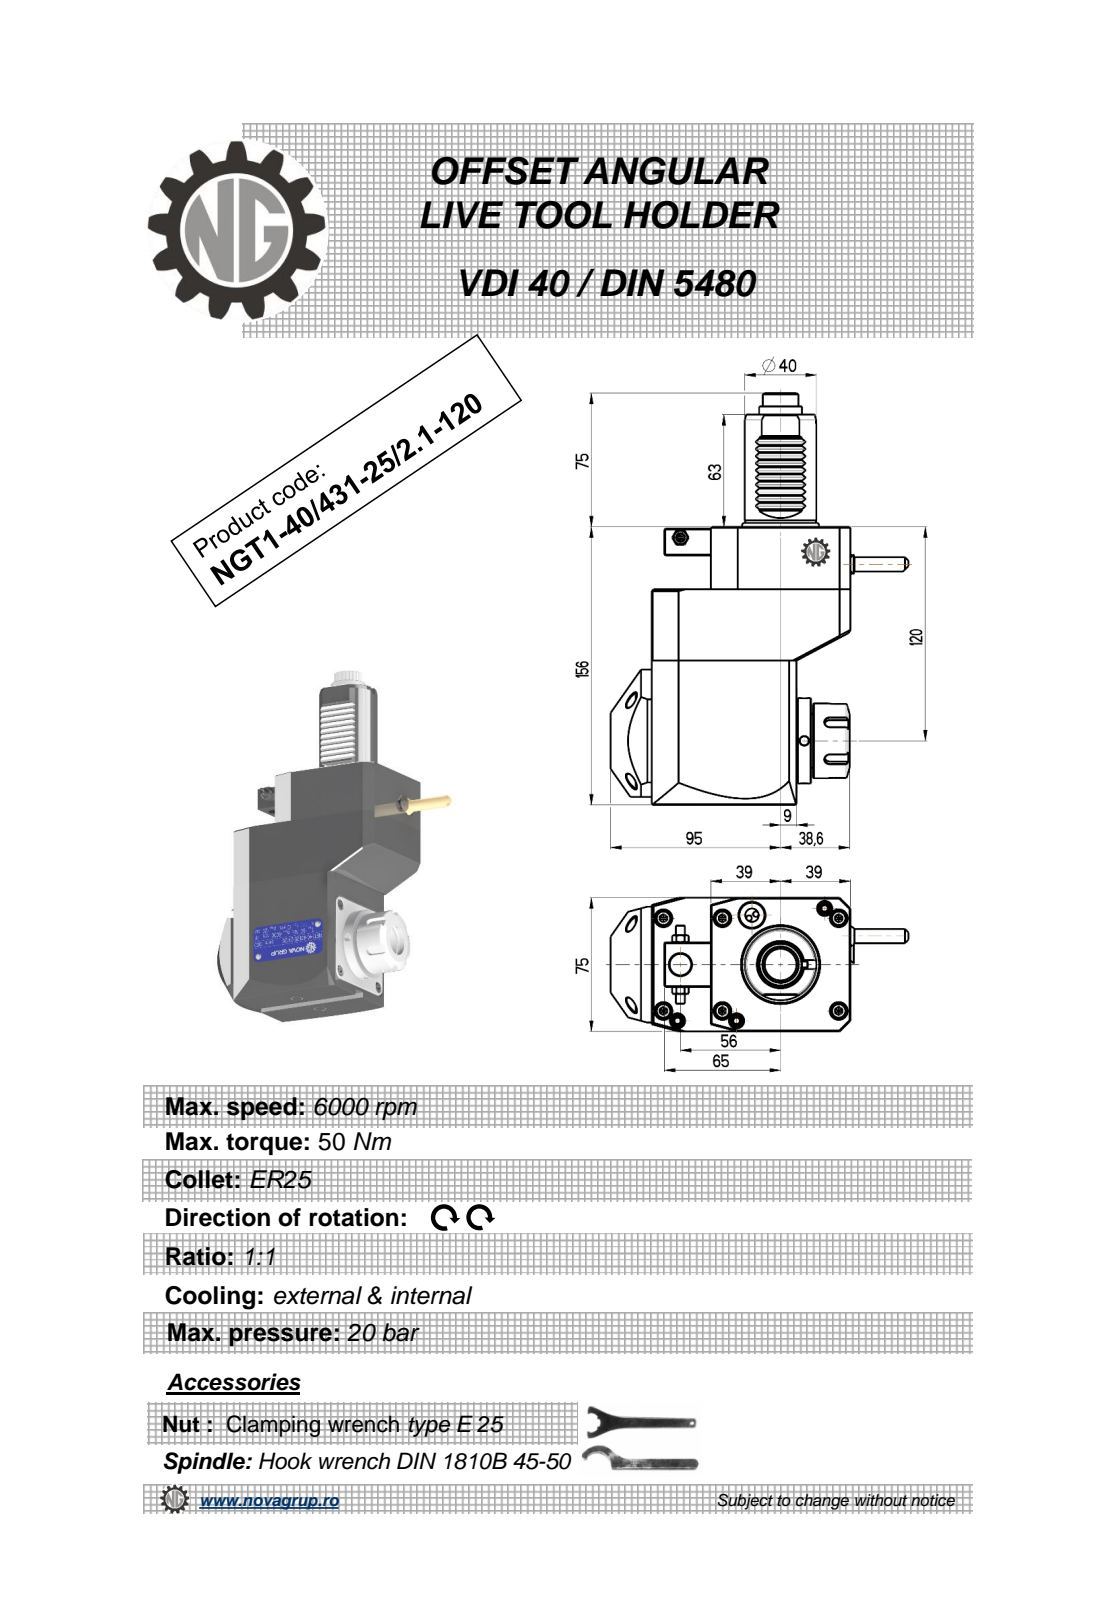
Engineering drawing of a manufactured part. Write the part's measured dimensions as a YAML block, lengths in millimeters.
part_name: "NGT1_40_431_25_2_1_120"
step_written_by: "PRO/ENGINEER BY PARAMETRIC TECHNOLOGY CORPORATION, 2010280 (CONFIG_CONTROL_DESIGN)"
units: millimeters
bodies: {solids: 1, faces: 573, planar: 212, cylindrical: 185, other: 176}
overall_size: [231, 166.5, 76.6]
volume: 1189000
surface_area: 87950
round_holes:
  - {diameter: 5, count: 3}
  - {diameter: 3, count: 1}
  - {diameter: 4.2, count: 1}
  - {diameter: 9.5, count: 1}
  - {diameter: 12, count: 1}
  - {diameter: 20.3, count: 1}
round_bosses_or_shafts:
  - {diameter: 48, count: 1}
  - {diameter: 42, count: 1}
  - {diameter: 40, count: 1}
  - {diameter: 37.5, count: 1}
  - {diameter: 33, count: 1}
  - {diameter: 24, count: 1}
  - {diameter: 11.2, count: 1}
  - {diameter: 8.96, count: 1}
partial_cylinders:
  - {radius: 2.08, count: 48}
  - {radius: 0.26, count: 12}
  - {radius: 0.3, count: 10}
  - {radius: 0.22, count: 6}
  - {radius: 3, count: 5}
  - {radius: 9.08, count: 1}
  - {radius: 9.92, count: 1}
  - {radius: 15, count: 1}
face_to_face_distances: [75, 156, 111, 30, 35, 121, 81, 33, 48, 78]
hole_center_spacings: [20.3, 69.25, 100.28, 111.5, 133.39]
